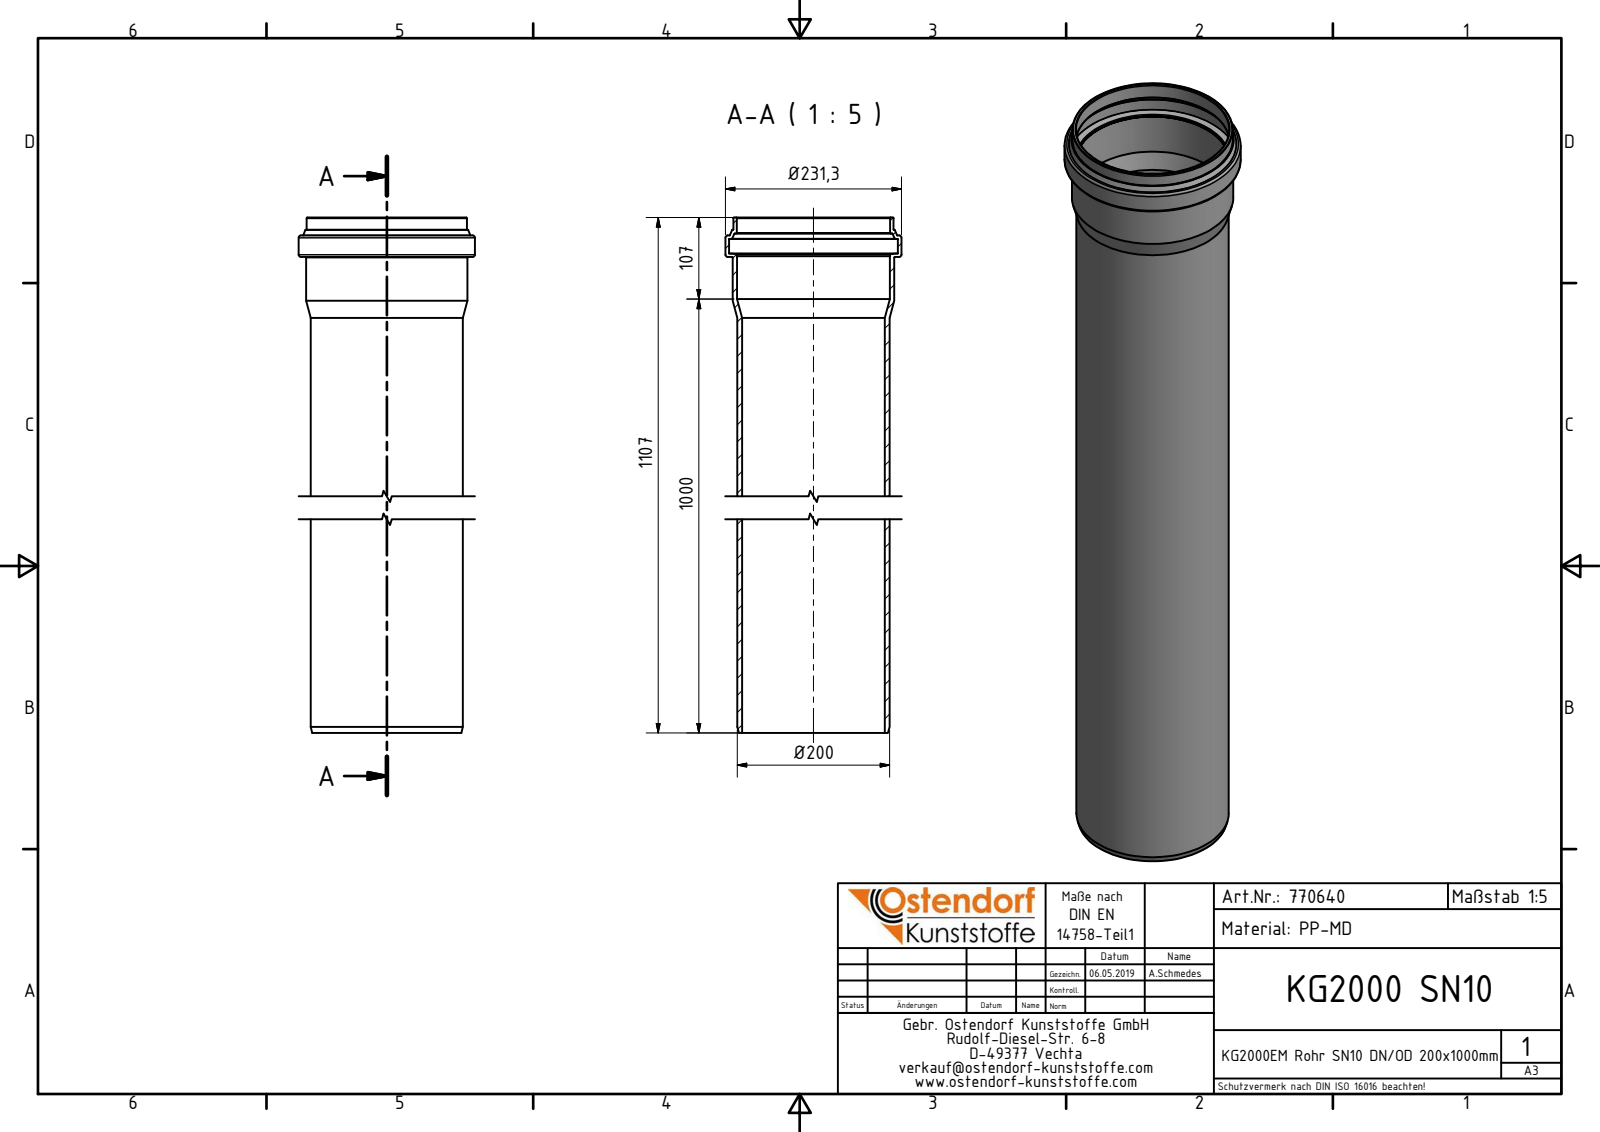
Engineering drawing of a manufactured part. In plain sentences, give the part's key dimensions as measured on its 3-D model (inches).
The part is named "770640 KG2000EM Rohr SN10 DN-OD200x1000". Its 3-D file was written by "Autodesk Inventor 2016 (AUTOMOTIVE_DESIGN)". It is 1 solid with 37 faces: 6 planar, 9 cylindrical and 22 other. Overall it measures 43.583 by 9.106 by 9.106 inches. Its volume is 255.7 cubic inches and its surface area 2 150 square inches. Round holes: 1 of diameter 7.386, 1 of diameter 7.906, 1 of diameter 7.913, 1 of diameter 8.736. Round bosses or shafts: 1 of diameter 9.106, 1 of diameter 8.346, 1 of diameter 8.283, 1 of diameter 7.874. The main face-to-face distances are 41.547, 42.657, 1.11, 43.583, 2.035, 0.925, 42.952, 1.404, 0.294, 0.631.
